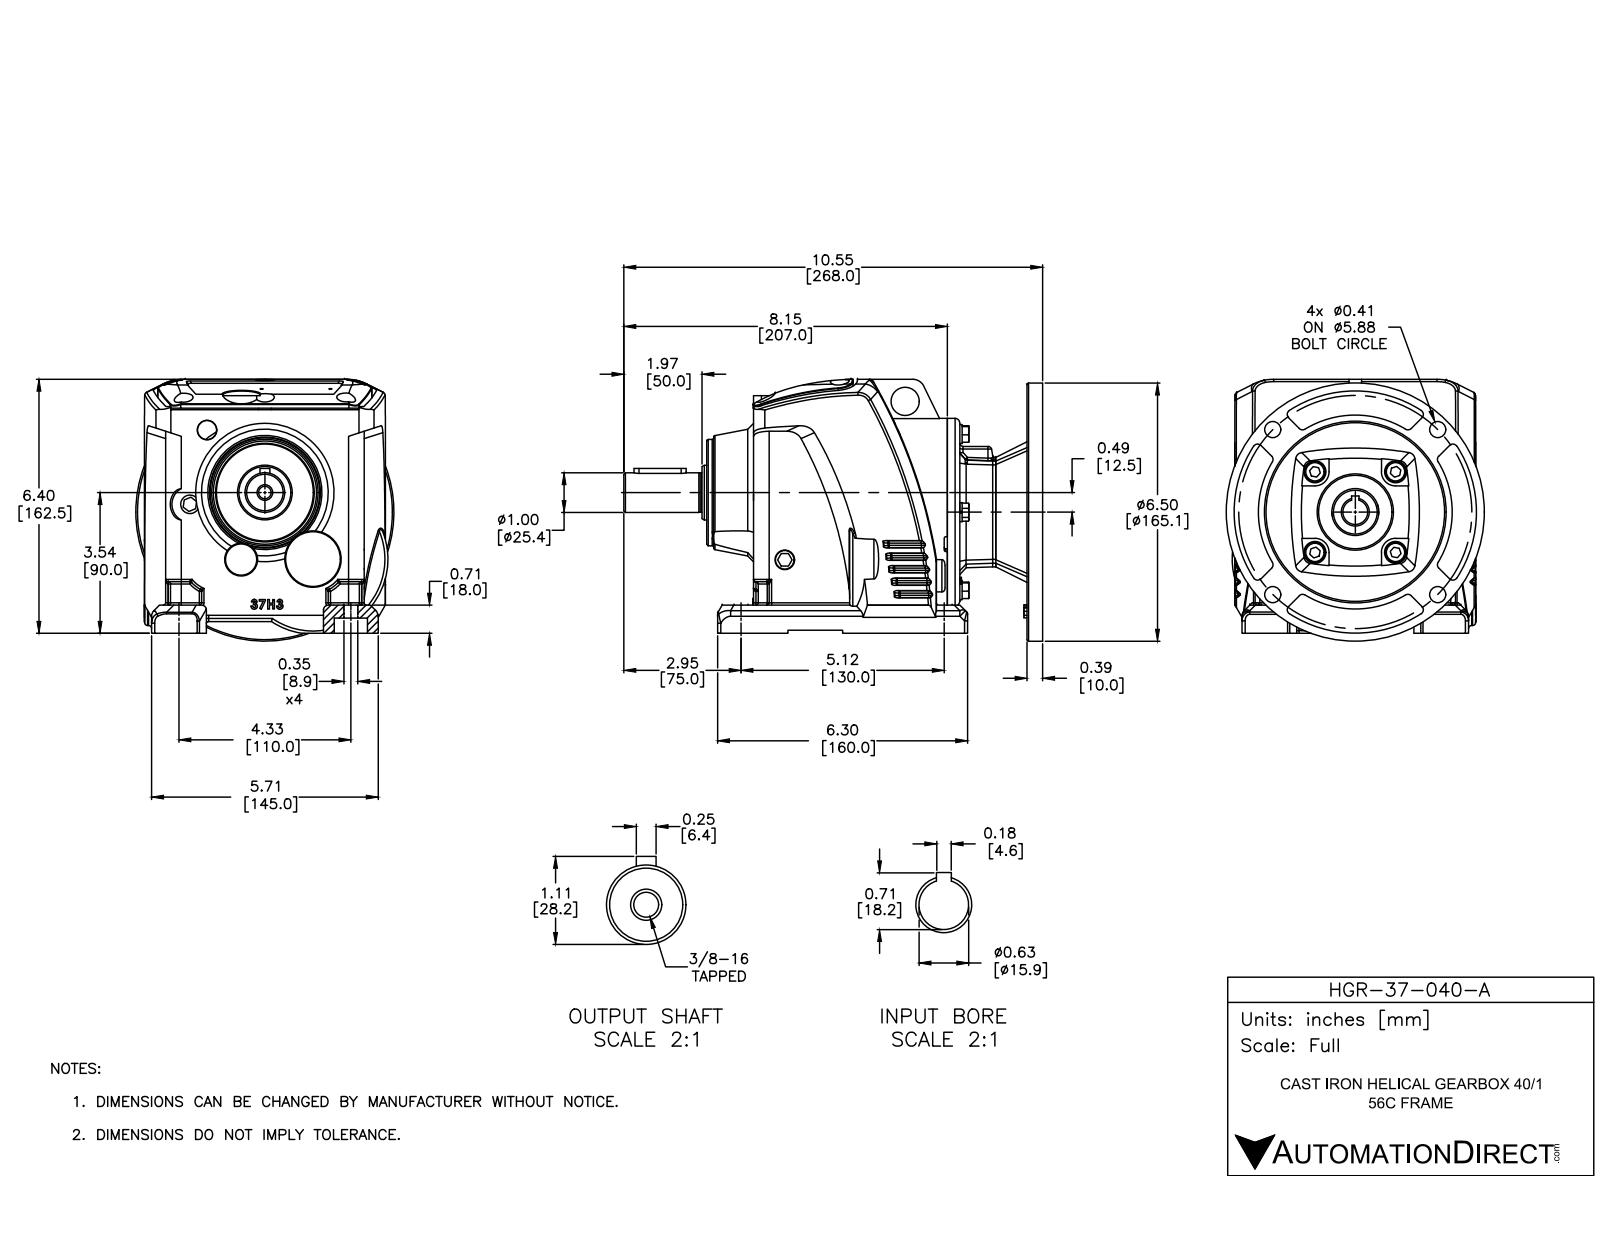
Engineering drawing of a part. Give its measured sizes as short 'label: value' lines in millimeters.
name: HGR-37-040-A
written by: SolidWorks 2015 (AUTOMOTIVE_DESIGN)
unit: mm
bodies: 4 solids, 1036 faces (343 planar, 277 cylindrical, 416 other)
size: 268 × 167.5 × 165.1
volume: 2 781 000 mm³; area: 247 600 mm²
holes: 6× ⌀12, 4× ⌀10.3, 4× ⌀14, 3× ⌀7, 2× ⌀2, 2× ⌀9, 2× ⌀10, 1× ⌀8, 1× ⌀15.9, 1× ⌀18, 1× ⌀24, 1× ⌀30
bosses: 4× ⌀13, 4× ⌀12.2, 4× ⌀8, 2× ⌀35, 2× ⌀12, 1× ⌀165.1, 1× ⌀120, 1× ⌀68
rounds: 43× R1.5, 21× R3, 18× R2, 8× R5, 6× R9, 6× R10, 5× R8, 4× R7
face distances: 181, 6, 7, 10, 175, 28, 110, 4, 53, 2
hole spacings: 83.1, 36.5, 38.1, 51.6, 74.6, 105.5, 111.1, 29
